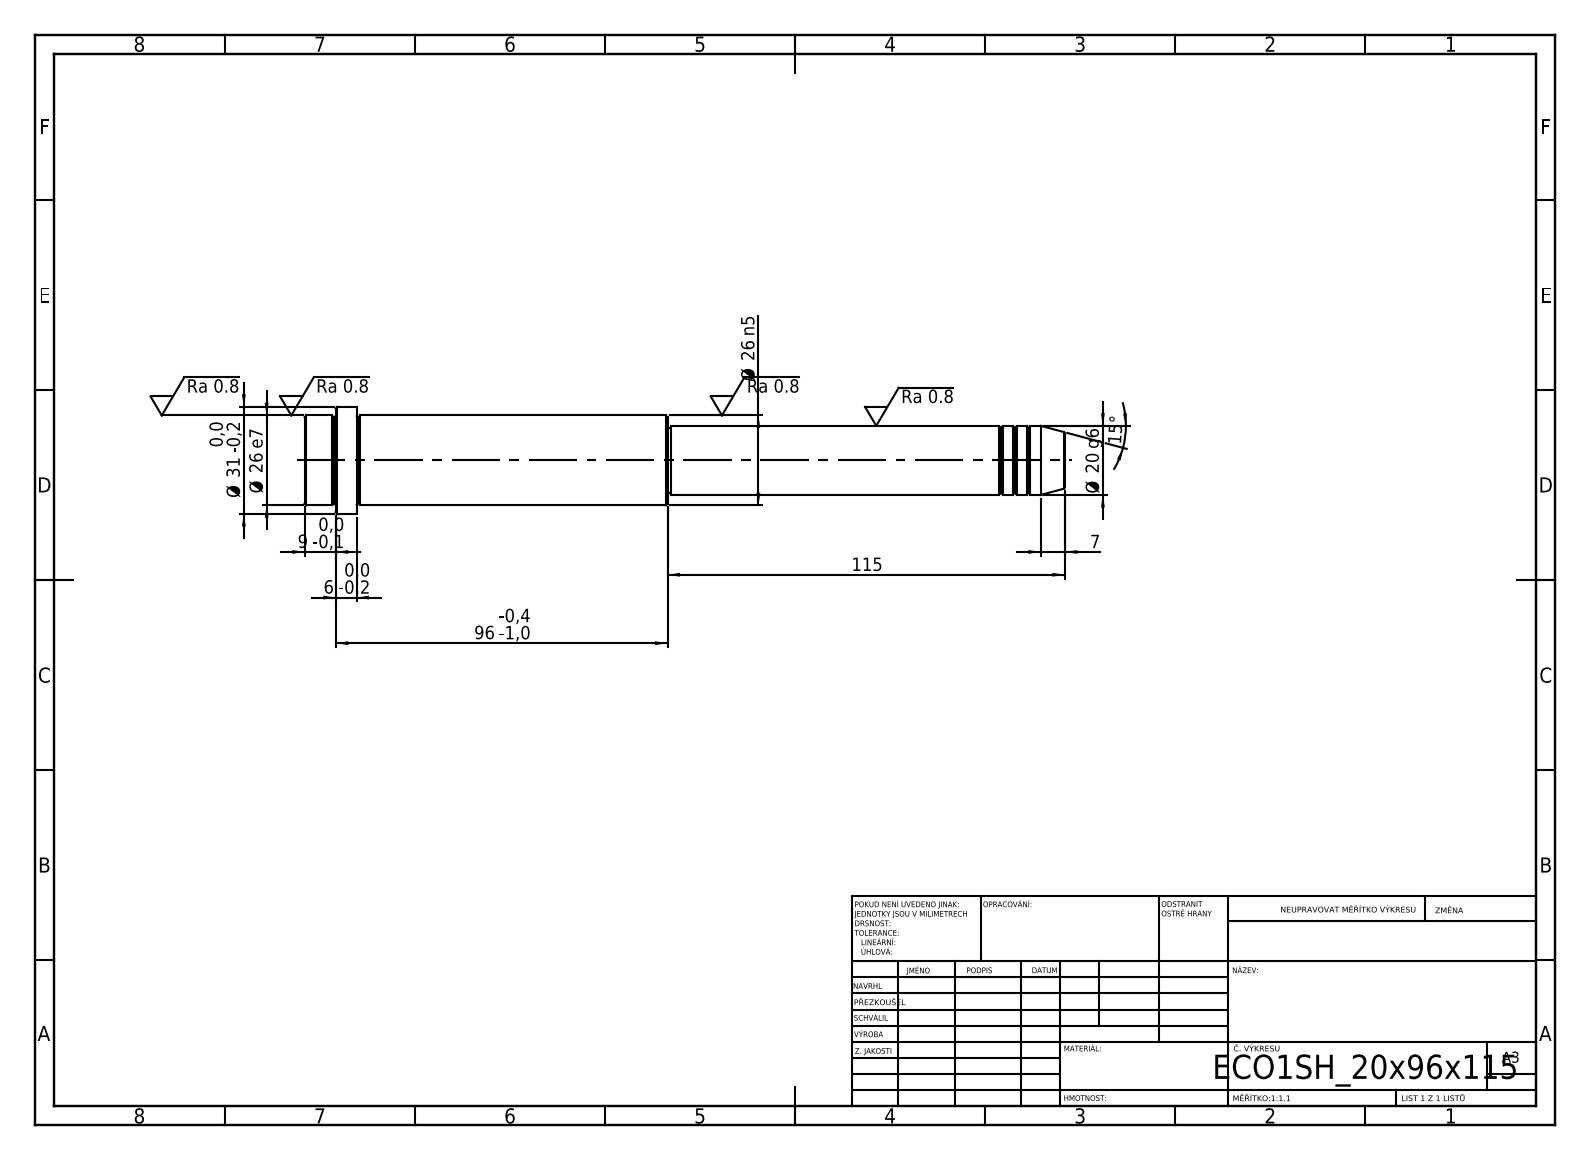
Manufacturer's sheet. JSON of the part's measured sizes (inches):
{"step_written_by": "SolidWorks 2019 (CONFIG_CONTROL_DESIGN)", "units": "inches", "bodies": {"solids": 1, "faces": 52, "planar": 6, "cylindrical": 16, "other": 30}, "overall_size": [8.661, 1.22, 1.22], "volume_in3": 5.653, "surface_area_in2": 27.02, "round_bosses_or_shafts": [[1.22, 1], [1.024, 1], [0.787, 1], [0.748, 1]], "face_to_face_distances": [0.591, 3.543, 4.134, 4.528, 8.071, 8.661, 8.307, 3.78, 0.236, 0.354]}
